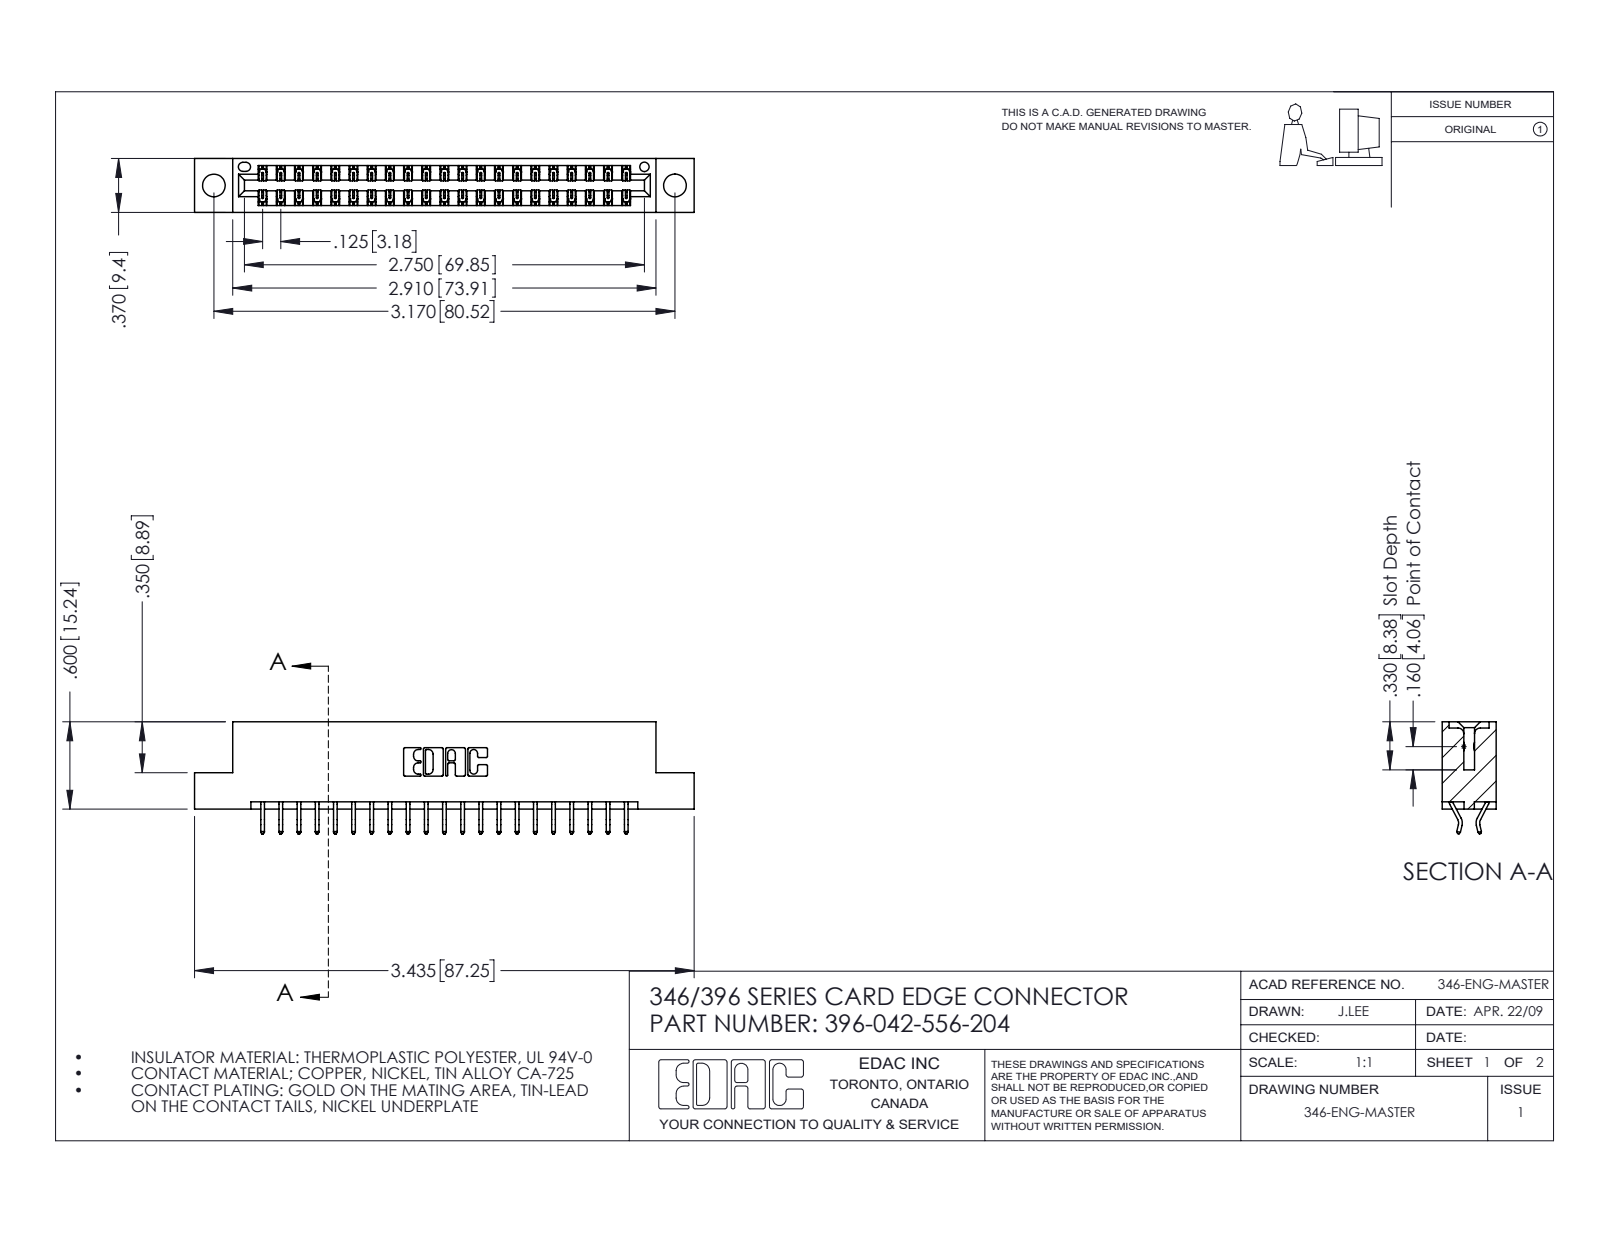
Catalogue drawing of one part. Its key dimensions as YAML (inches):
part_name: "346 Part_Flush Mounting Lugs - 0.156 Dia-TH; 345-292-001_556 Tail; 396-042-556-204"
step_written_by: "SolidWorks 2016 (CONFIG_CONTROL_DESIGN)"
units: inches
bodies: {solids: 43, faces: 2558, planar: 1714, cylindrical: 844, other: 0}
overall_size: [3.435, 0.77, 0.37]
volume: 0.504
surface_area: 16.73
round_holes:
  - {diameter: 0.156, count: 2}
  - {diameter: 0.064, count: 1}
partial_cylinders:
  - {radius: 0.006, count: 63}
  - {radius: 0.01, count: 22}
  - {radius: 0.007, count: 6}
  - {radius: 0.031, count: 6}
  - {radius: 0.026, count: 3}
  - {radius: 0.01, count: 2}
  - {radius: 0.014, count: 2}
  - {radius: 0.022, count: 2}
face_to_face_distances: [0.048, 0.322, 0.25, 0.37, 0.025, 0.072, 0.298, 0.275, 0.148, 0.222]
hole_center_spacings: [0.246, 2.963, 3.17]
